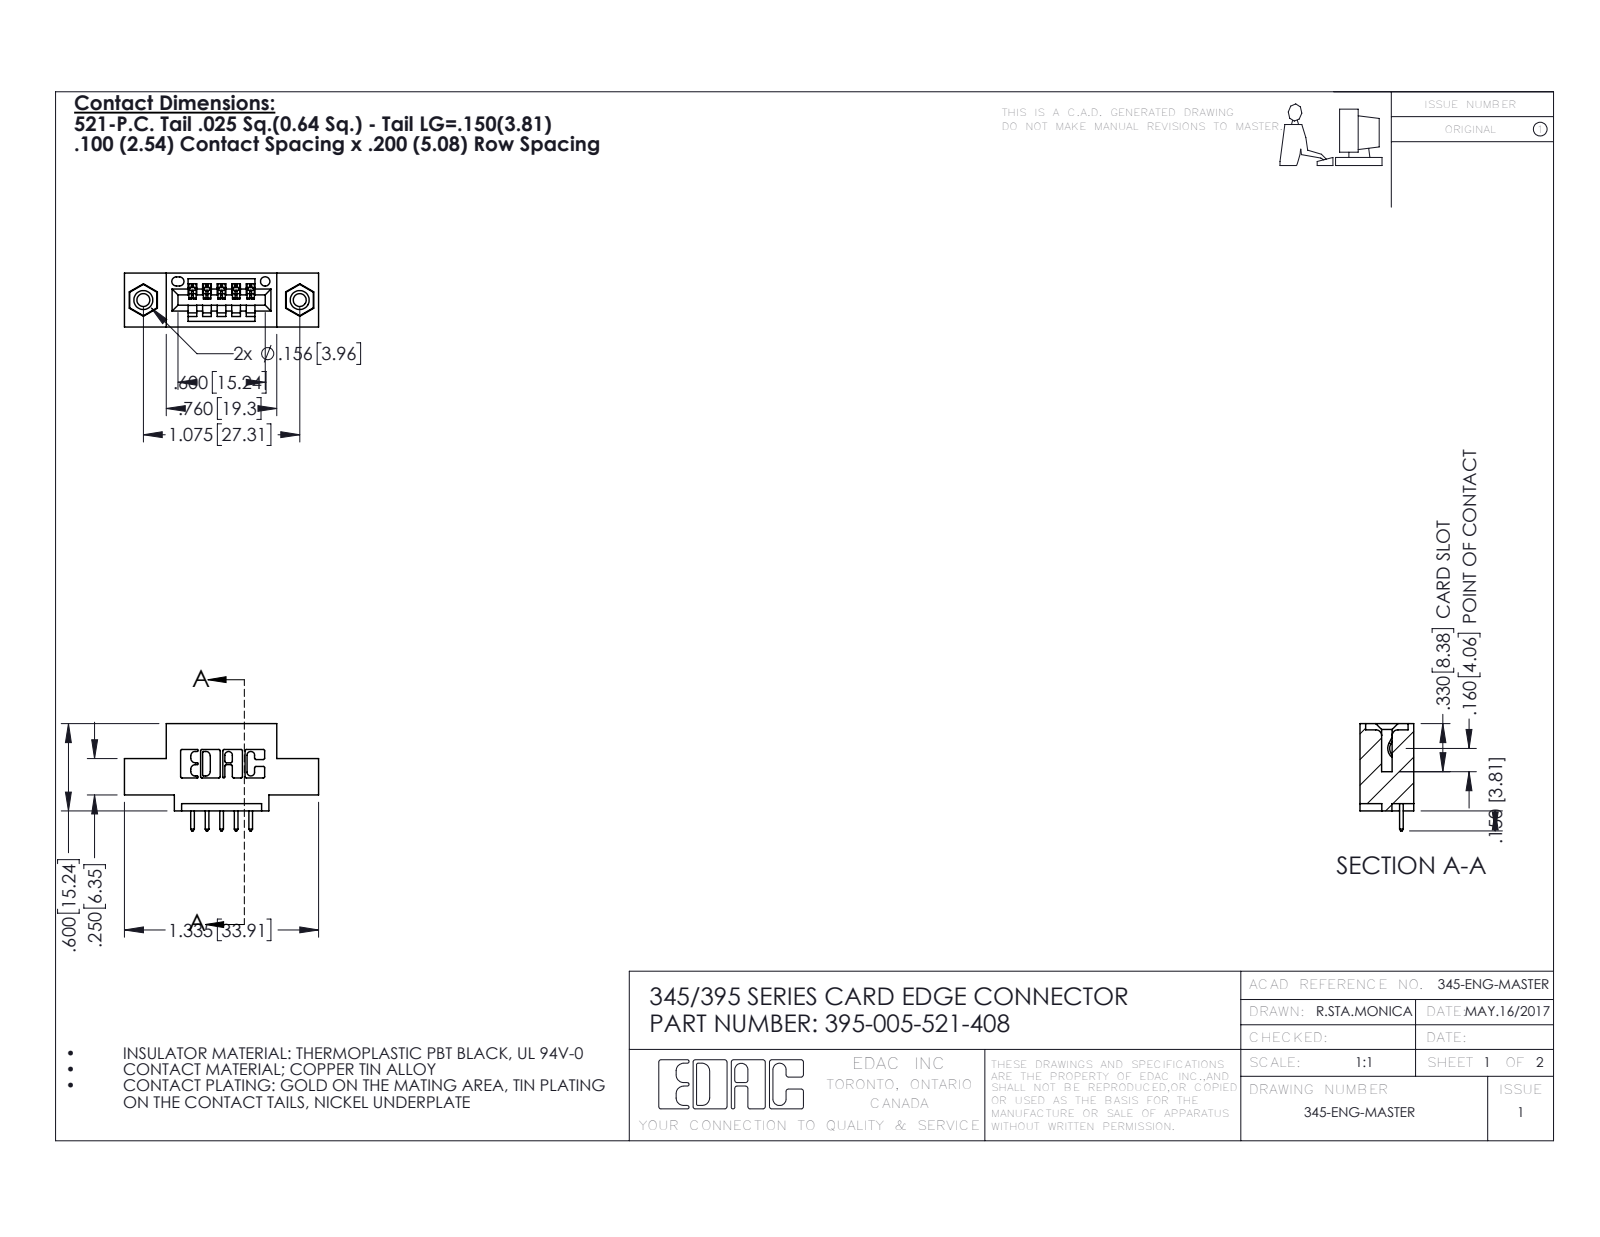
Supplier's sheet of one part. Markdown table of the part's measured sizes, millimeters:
| quantity | value |
| --- | --- |
| part name | 345-292-001_345-293-121; 345 Part_0.110 Offset - 0.156 Dia-TI; 345-250-001_345-250-003-102; 395-005-521-408 |
| STEP written by | SolidWorks 2016 (CONFIG_CONTROL_DESIGN) |
| units | millimeters |
| bodies | 8 solids, 480 faces (316 planar, 148 cylindrical, 16 other) |
| overall size | 33.9 × 18.7 × 9.4 |
| volume | 2 820 mm³ |
| surface area | 3 295 mm² |
| round holes (diameter × count) | 2.3 × 2, 3.2 × 2, 4 × 2, 1.6 × 1 |
| round bosses / shafts (diameter × count) | 3.9 × 2 |
| partial cylindrical surfaces (radius × count) | 0.3 × 22, 0.2 × 10, 0.3 × 10, 0.2 × 6, 0.8 × 6, 0.7 × 3, 0.8 × 2, 1 × 2 |
| main face-to-face distances | 5.1, 9.4, 1.8, 7.6, 2.5, 0.6, 6.4, 2.5, 6.9, 1.5 |
| hole center spacings | 6.9, 21.5, 27.3 |
